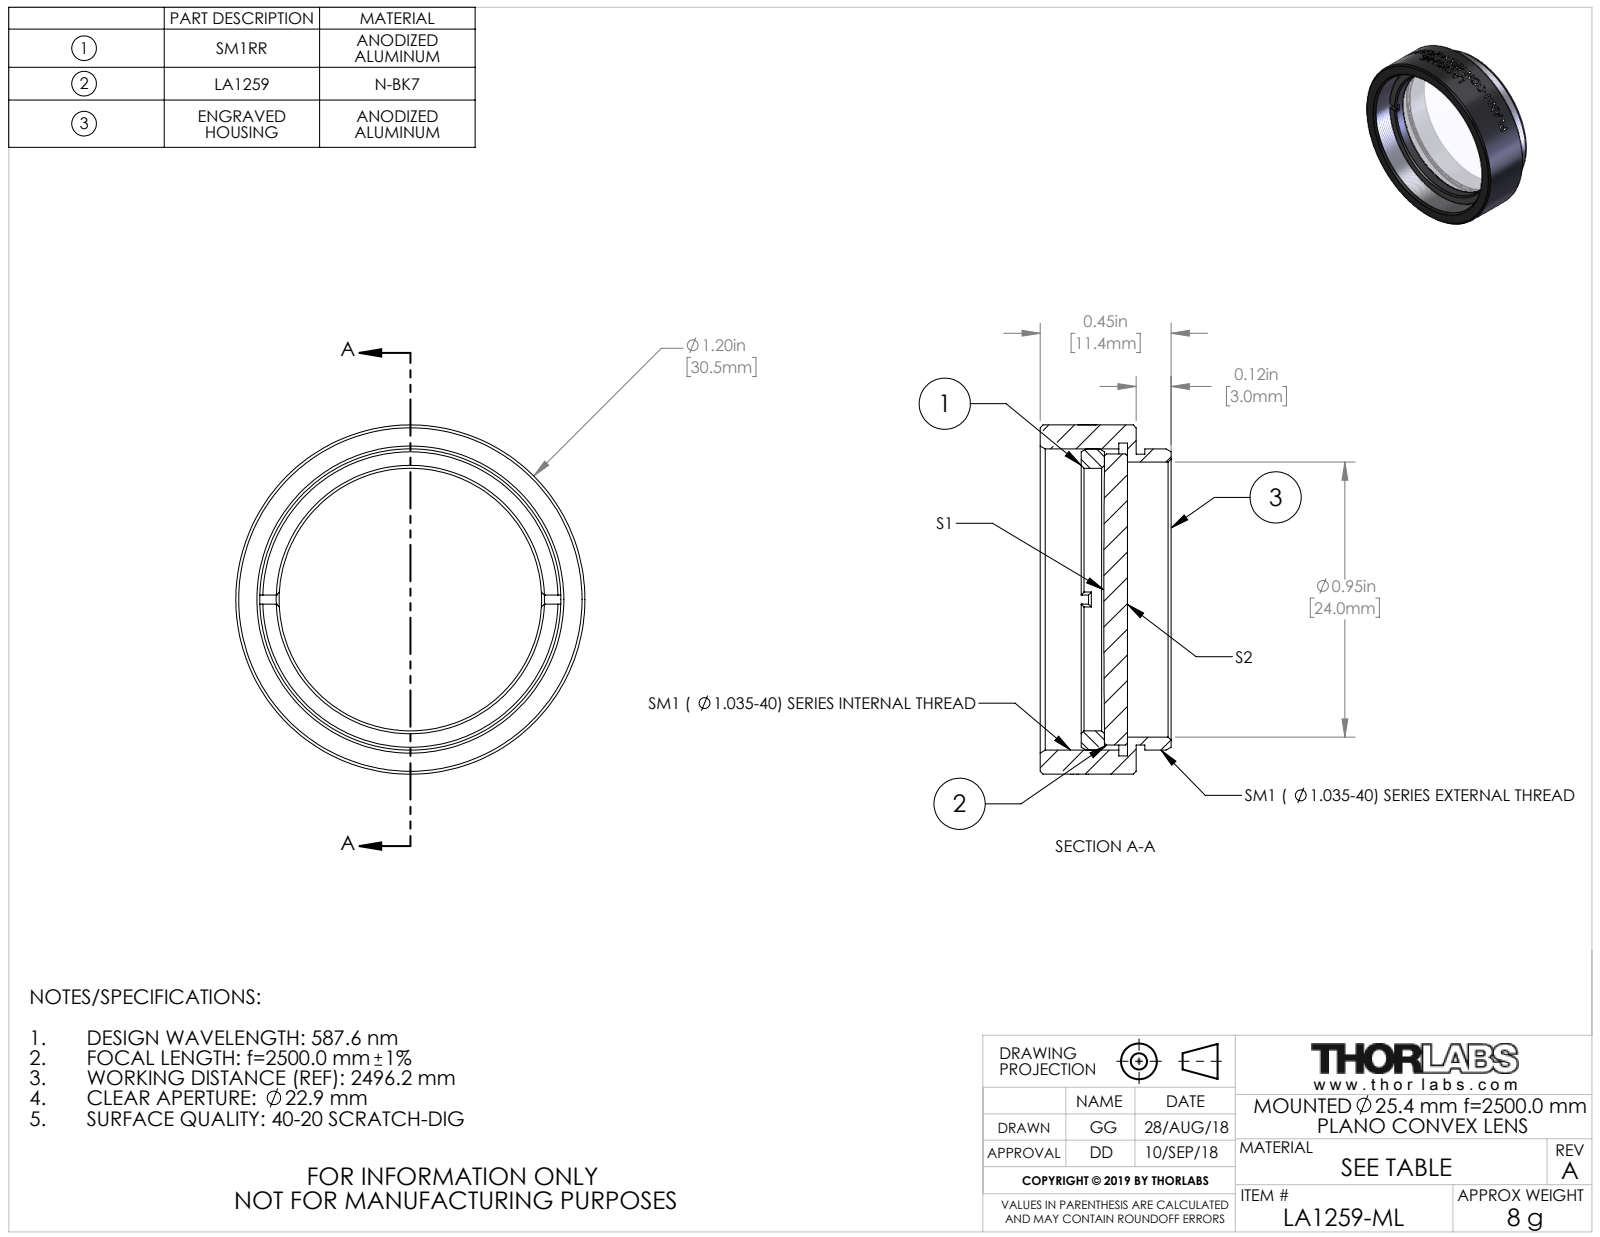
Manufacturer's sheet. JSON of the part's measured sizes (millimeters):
{"part_name": "TTN162143-E0W", "step_written_by": "SolidWorks 2018 (CONFIG_CONTROL_DESIGN)", "units": "millimeters", "bodies": {"solids": 3, "faces": 138, "planar": 20, "cylindrical": 90, "other": 28}, "overall_size": [30.48, 30.48, 11.43], "volume_mm3": 3107, "surface_area_mm2": 4296, "round_holes": [[22.91, 1], [24, 1], [27.3, 1]], "round_bosses_or_shafts": [[30.48, 1], [26.29, 1], [25.4, 1], [25.37, 1]], "face_to_face_distances": [0.77, 8.39, 7.62, 2.77, 2, 5.62, 4.8, 4.03, 2.03, 3.59]}
